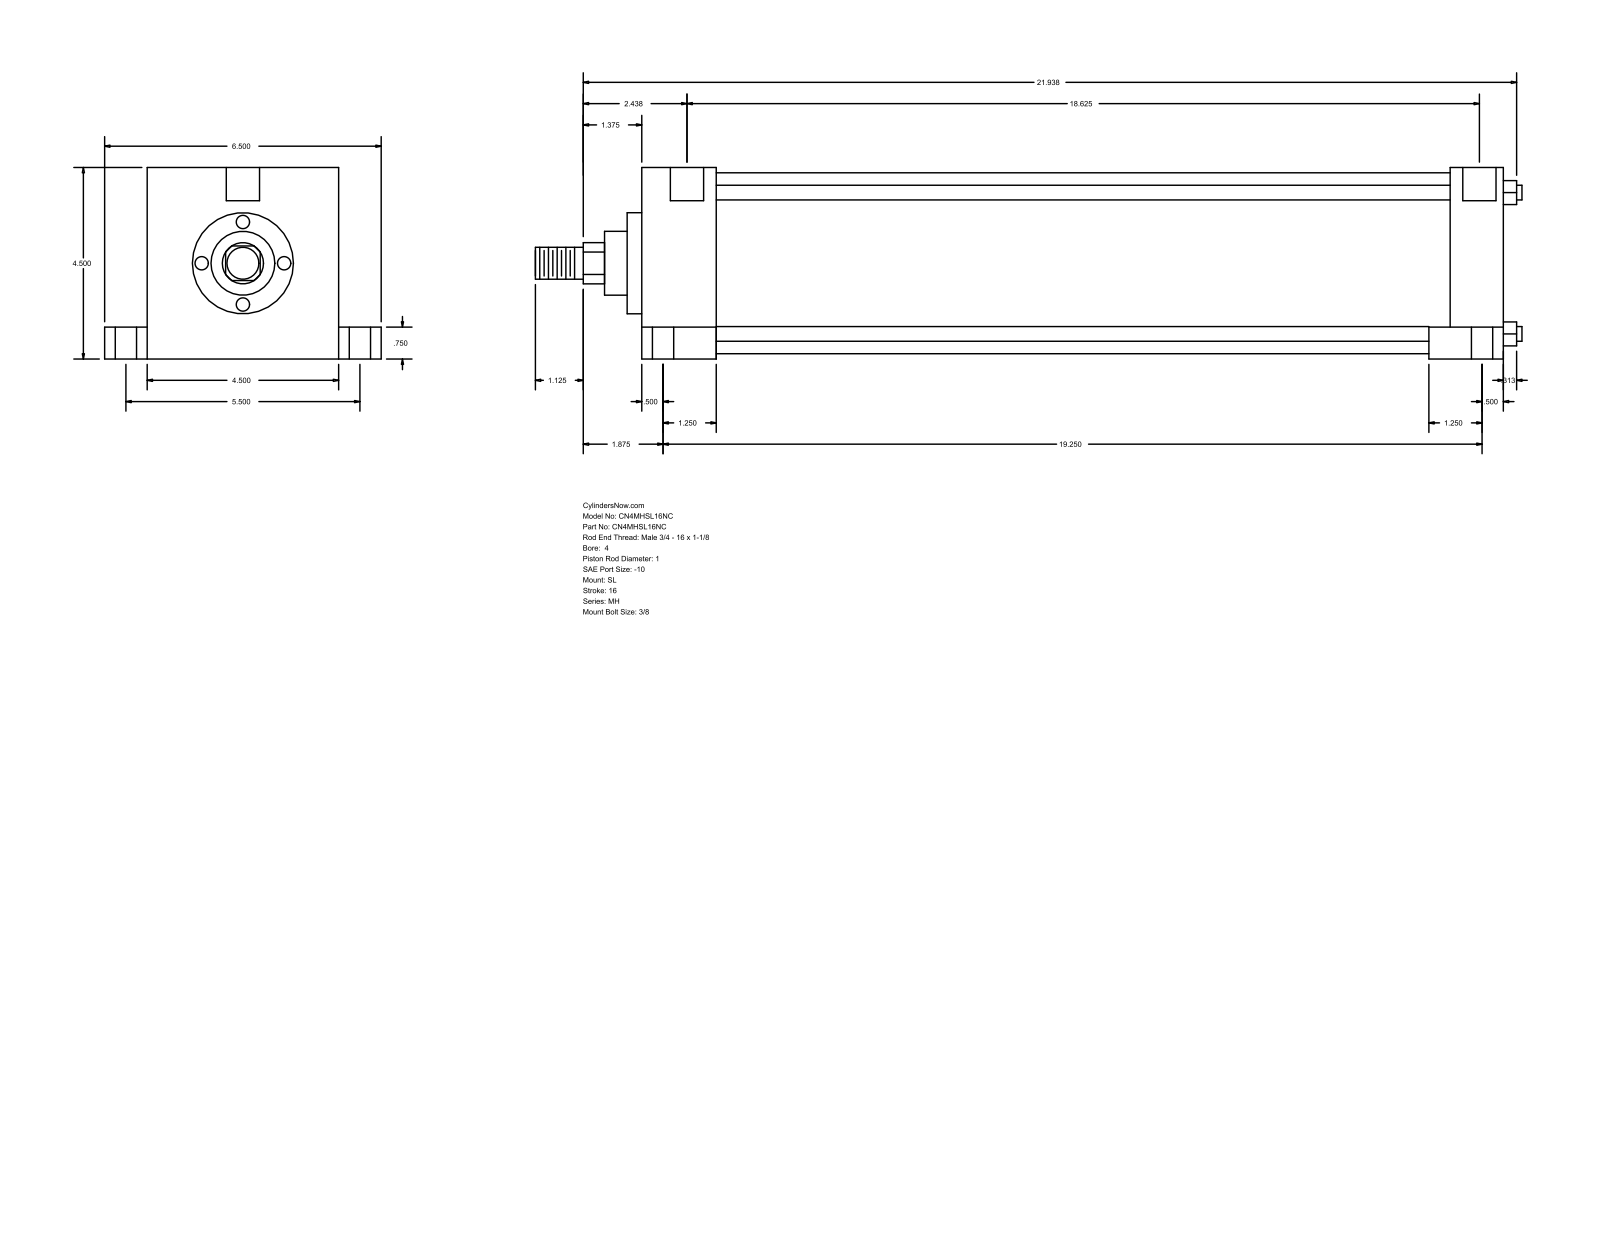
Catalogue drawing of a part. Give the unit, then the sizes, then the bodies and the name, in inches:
Units: inches
Overall size (bounding box): 23.187 × 6.5 × 4.5
Round holes (diameter × count): ⌀0.344 ×4, ⌀0.5 ×4, ⌀0.75 ×4, ⌀0.781 ×2
Round bosses / shafts (diameter × count): ⌀0.345 ×4, ⌀4.25 ×1, ⌀2.375 ×1, ⌀1.5 ×1, ⌀1 ×1, ⌀0.75 ×1
Partial cylindrical surfaces — rounded edges, fillets, slot ends (radius × count): R0.484 ×1
Main face-to-face distances: 4.5, 20.25, 1.75, 18.5, 19, 17.25, 1.25, 1, 5.5, 0.75
Hole centre spacings: 2.75, 2.751, 2.795, 2.807, 5.5, 18.75, 18.889, 18.951
Bodies: 0 solids, 110 faces (77 planar, 33 cylindrical, 0 other)
Part name (STEP PRODUCT): MH_SL__0400_1
STEP written by: GSSL Pune (CONFIG_CONTROL_DESIGN)
